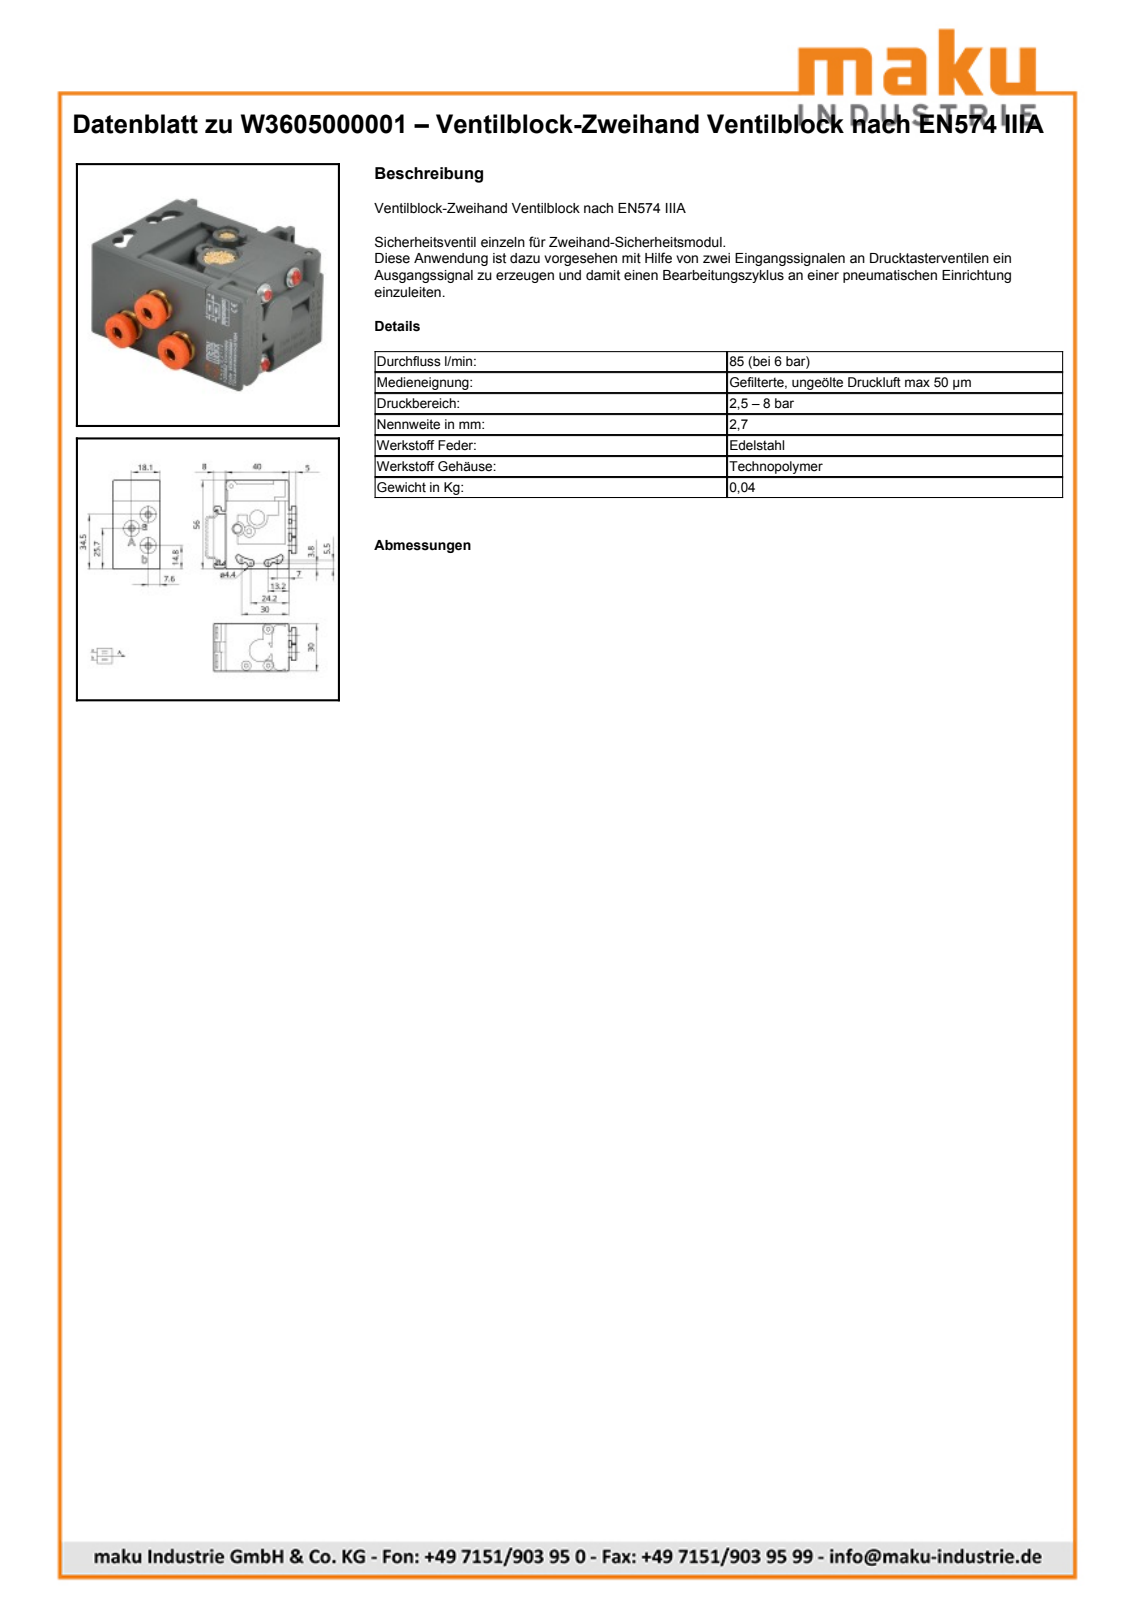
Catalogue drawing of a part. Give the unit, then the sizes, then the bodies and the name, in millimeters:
Units: millimetres
Overall size (bounding box): 50 × 45 × 30
Round holes (diameter × count): ⌀4 ×3, ⌀4.4 ×2, ⌀2.46 ×1, ⌀5 ×1, ⌀10 ×1
Round bosses / shafts (diameter × count): ⌀10 ×3, ⌀5.9 ×3, ⌀5.8 ×2
Partial cylindrical surfaces — rounded edges, fillets, slot ends (radius × count): R5 ×2
Main face-to-face distances: 30, 40, 50, 5, 45, 2, 3, 42, 39.8, 2.2
Hole centre spacings: 1.8, 7.65, 8.5, 9.35, 10.8, 11, 11.95, 12.6
Volume: 59 375 mm³ · Surface area: 11 368 mm²
Bodies: 1 solid, 71 faces (51 planar, 18 cylindrical, 2 other)
Part name (STEP PRODUCT): W3605000001
STEP written by: PARTsolutions (AUTOMOTIVE_DESIGN)
